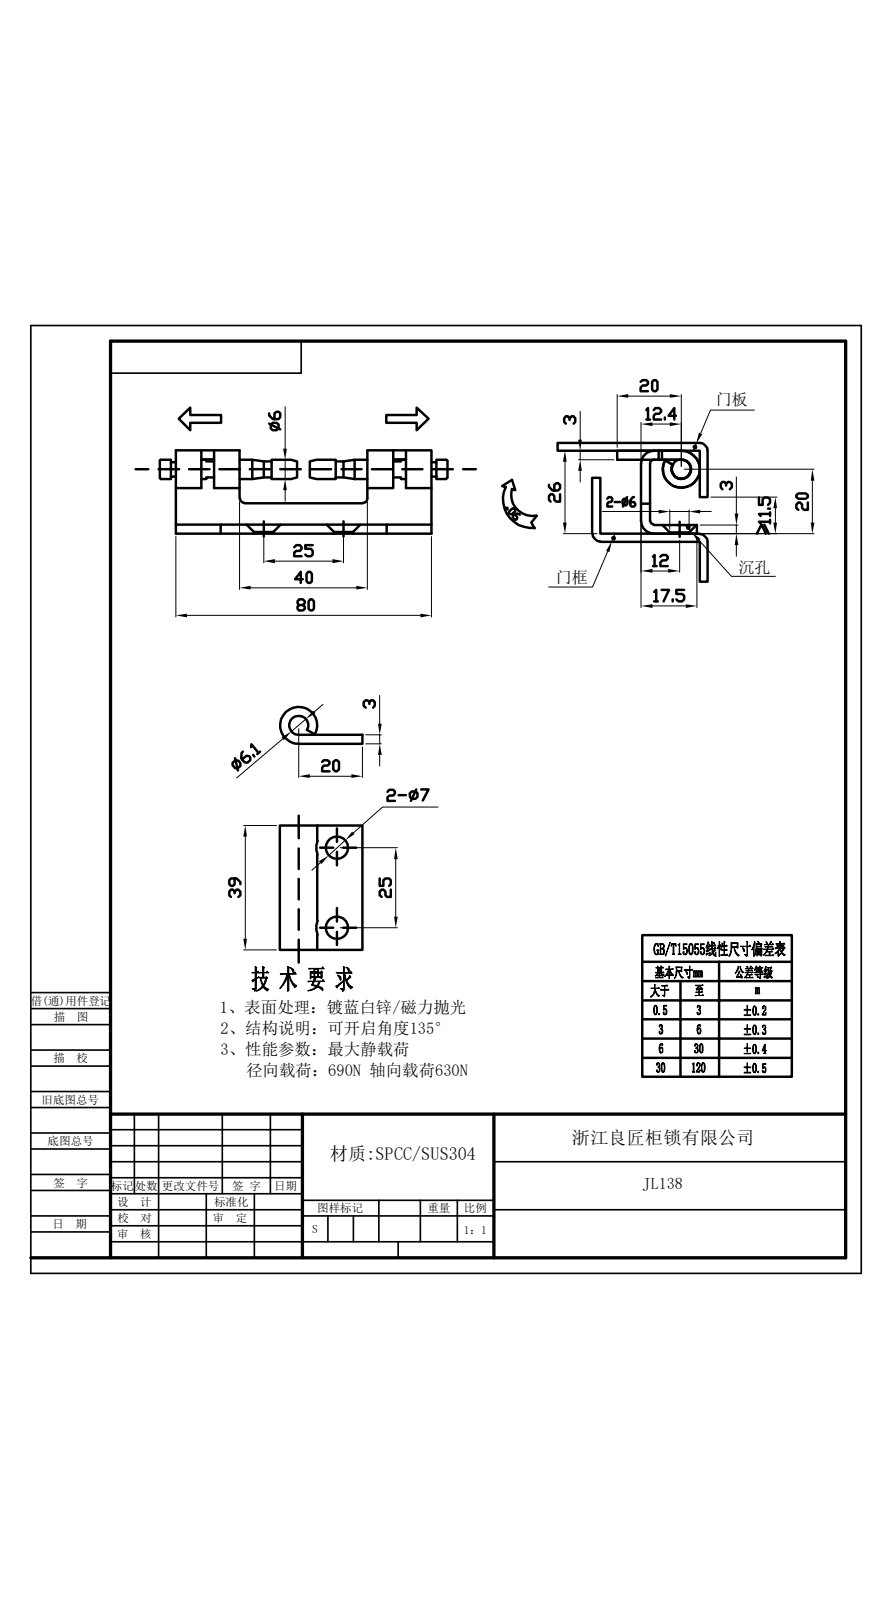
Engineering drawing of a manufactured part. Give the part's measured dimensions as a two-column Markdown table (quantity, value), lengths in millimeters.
| quantity | value |
| --- | --- |
| STEP written by | Rhino 8.5 (CONFIG_CONTROL_DESIGN) |
| units | millimeters |
| bodies | 4 solids, 140 faces (52 planar, 64 cylindrical, 24 other) |
| overall size | 90 × 26 × 25.8 |
| volume | 15 629 mm³ |
| surface area | 13 547 mm² |
| round holes (diameter × count) | 6 × 2, 7 × 2 |
| round bosses / shafts (diameter × count) | 11.6 × 1, 6 × 1, 5 × 1, 4.5 × 1 |
| partial cylindrical surfaces (radius × count) | 1 × 8, 2.8 × 4, 1.2 × 2, 4 × 2 |
| main face-to-face distances | 2.8, 23.2, 26, 20.4, 60, 12, 8, 20, 39.5, 20.5 |
| hole center spacings | 11.66, 25, 27.59 |
